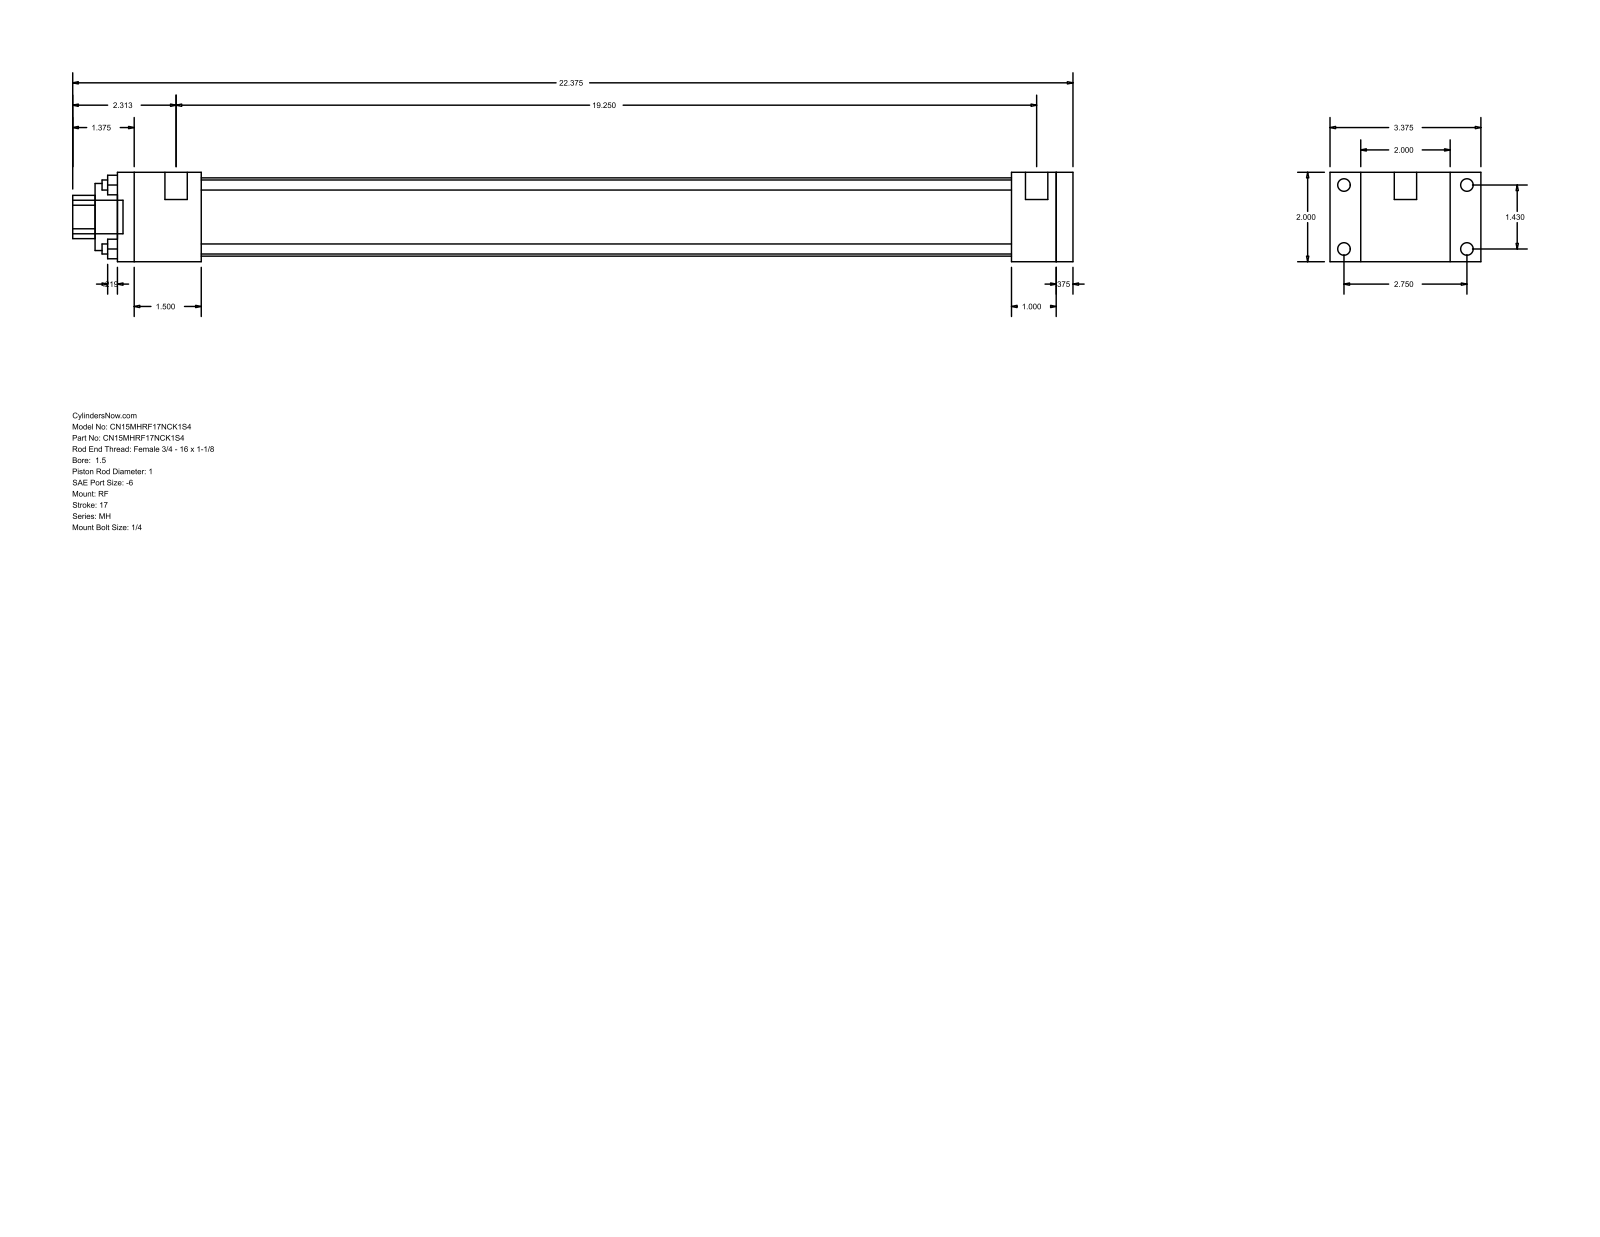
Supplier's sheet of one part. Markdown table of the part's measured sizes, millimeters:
| quantity | value |
| --- | --- |
| part name | MH_RF__0150_1 |
| STEP written by | GSSL Pune (CONFIG_CONTROL_DESIGN) |
| units | millimeters |
| bodies | 0 solids, 92 faces (64 planar, 28 cylindrical, 0 other) |
| overall size | 568.33 × 85.72 × 50.8 |
| round holes (diameter × count) | 5.71 × 4, 25.4 × 1, 38.1 × 1, 44.45 × 1 |
| round bosses / shafts (diameter × count) | 7.14 × 4, 5.56 × 4, 12.7 × 2, 19.05 × 1 |
| partial cylindrical surfaces (radius × count) | 12.29 × 1 |
| main face-to-face distances | 50.8, 9.53, 533.4, 25.4, 542.93, 17.46, 68.26, 508, 34.93, 47.63 |
| hole center spacings | 25.68, 36.32, 51.36 |
